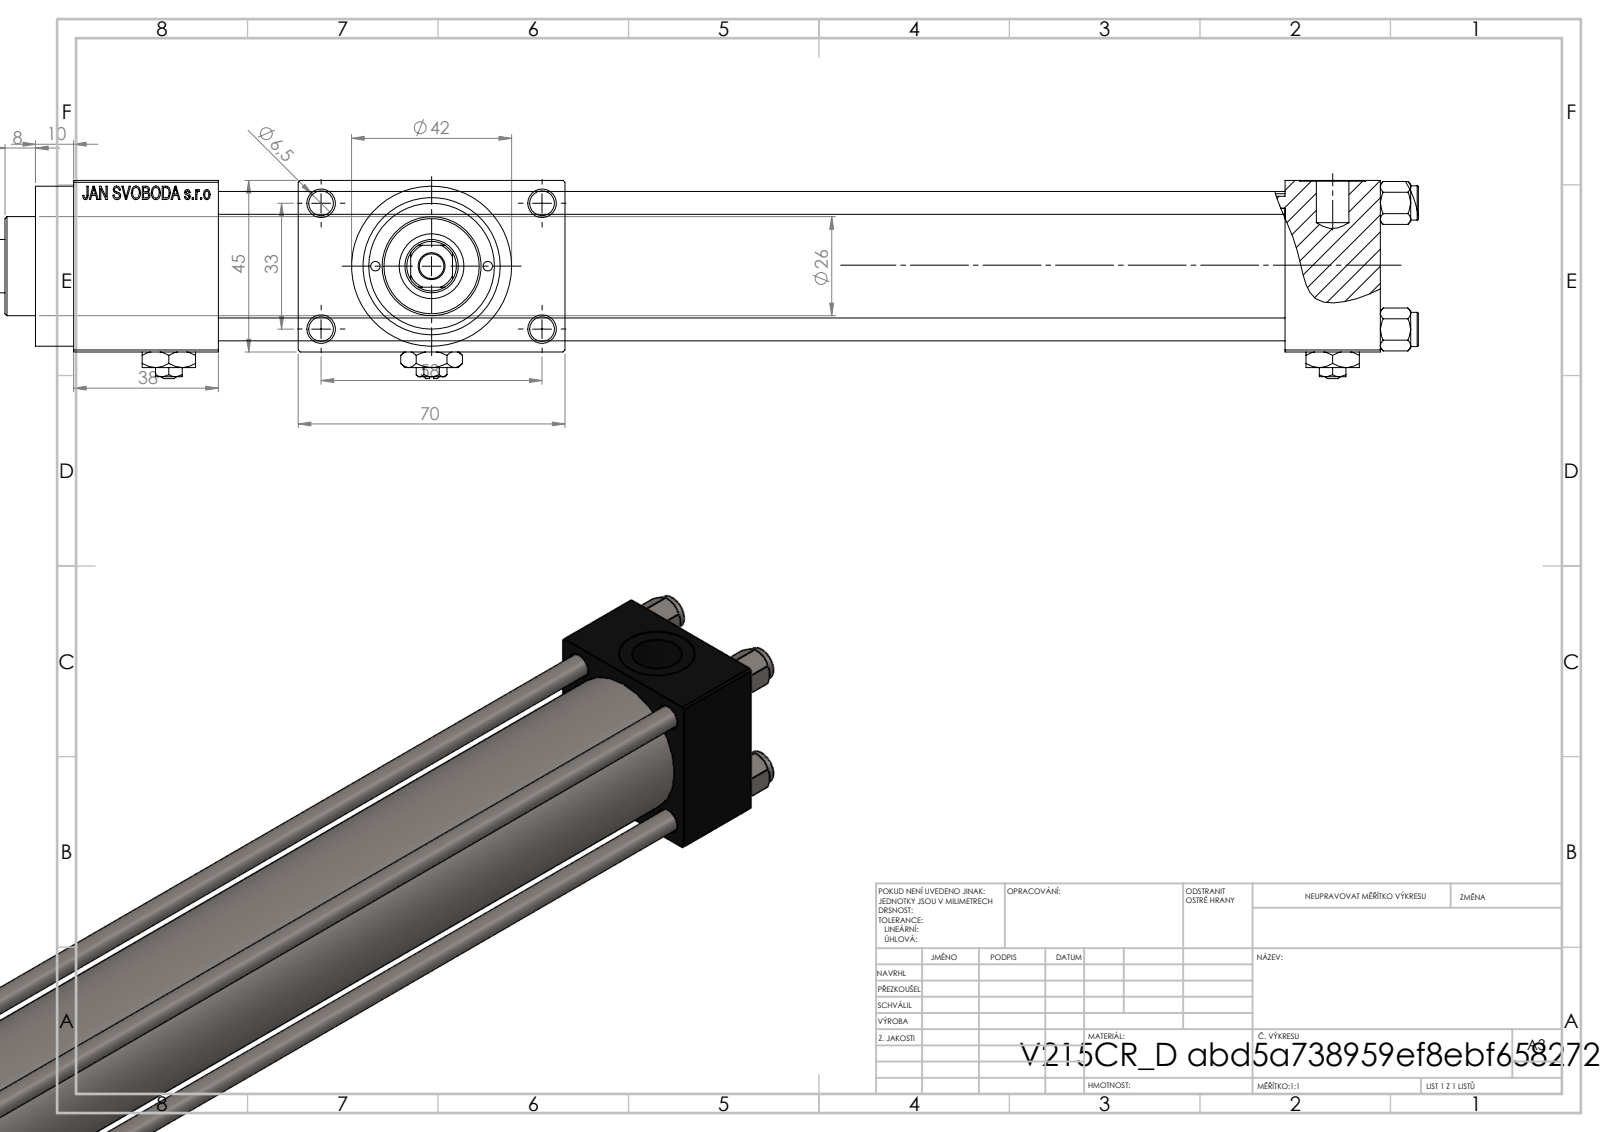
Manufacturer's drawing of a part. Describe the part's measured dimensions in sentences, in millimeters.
The part is named "V215CR_D_TYCINKA; Zatka_pro_OIL_PORT; V215CR_VCP_D; V215CR_D_Body (+2 more)". Its 3-D file was written by "SolidWorks 2019 (CONFIG_CONTROL_DESIGN)". It is 13 solids with 1210 faces: 544 planar, 104 cylindrical and 562 other. Overall it measures 388 by 70 by 52 millimeters. Its volume is 367 816 cubic millimeters and its surface area 154 644 square millimeters. Round holes: 5 of diameter 6.5, 4 of diameter 6, 2 of diameter 2.5, 2 of diameter 7, 2 of diameter 13.16, 2 of diameter 20, 1 of diameter 14, 1 of diameter 17, 1 of diameter 24, 1 of diameter 32, 1 of diameter 33. Round bosses or shafts: 4 of diameter 9, 1 of diameter 42, 1 of diameter 38, 1 of diameter 26. Partial cylindrical surfaces (rounded edges, fillets, slot ends): 1 of radius 6.5. The main face-to-face distances are 45, 25, 12.5, 57.5, 280, 305, 318, 70, 38, 343. The hole center spacings are 12.4, 16.7, 21.8, 23.48, 33.2, 33.37, 35.35, 35.47.
